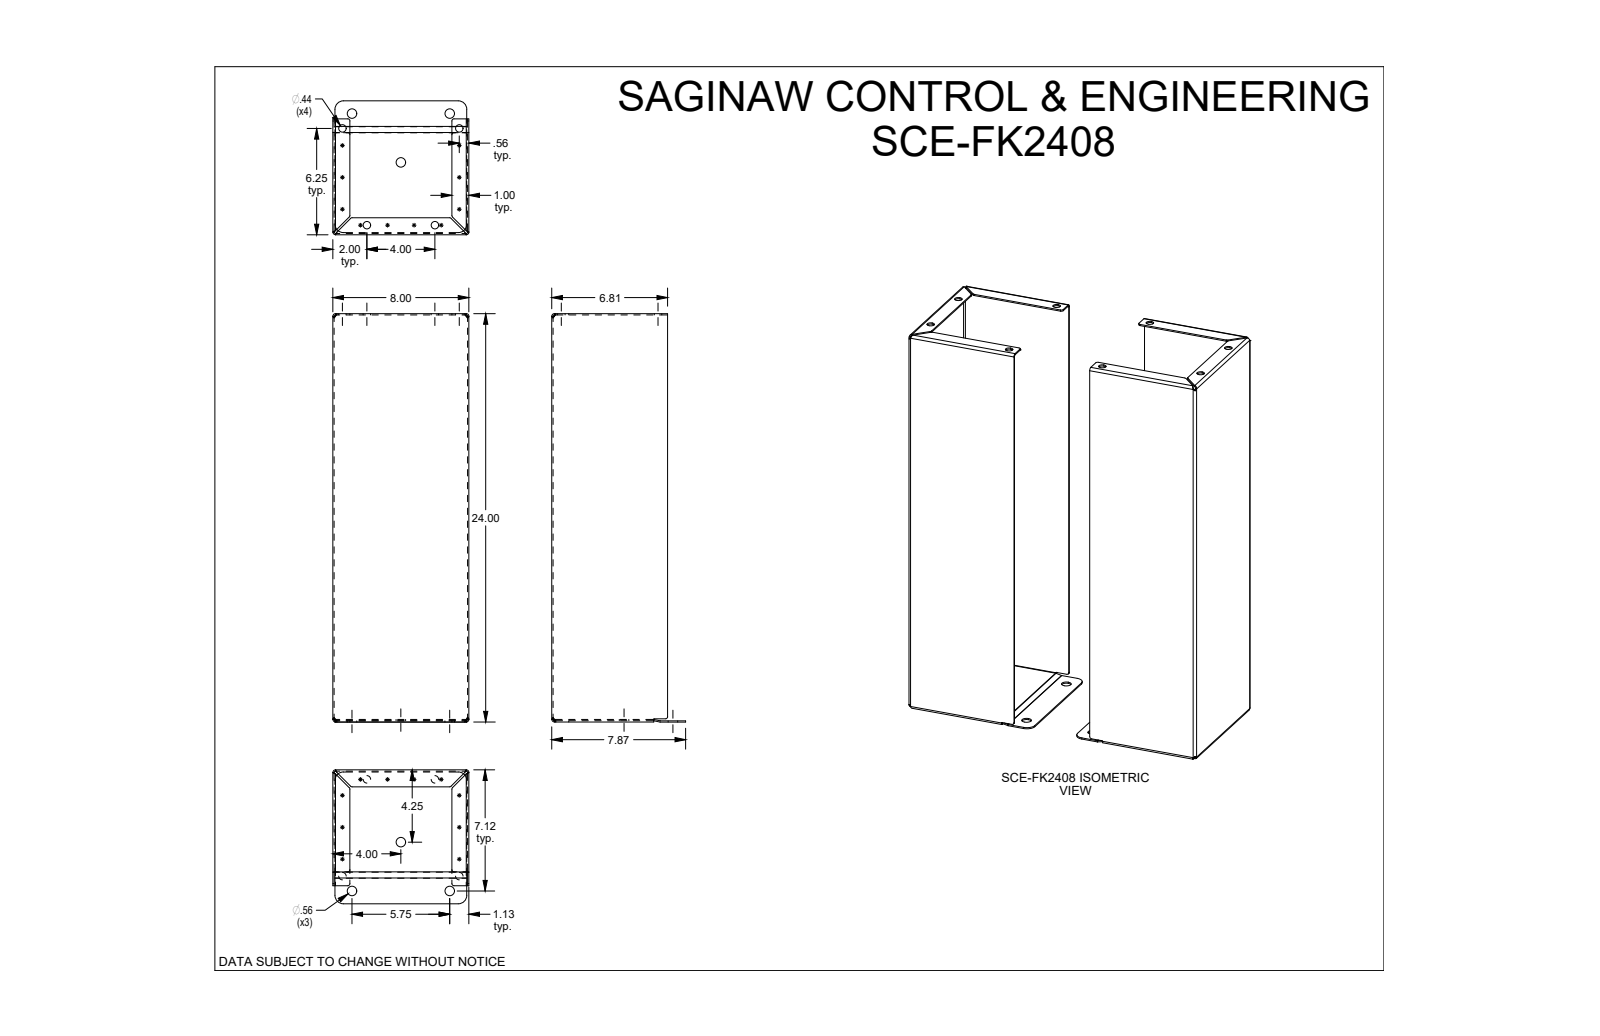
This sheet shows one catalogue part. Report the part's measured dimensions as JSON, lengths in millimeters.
{"part_name": "SCE-FK2408", "step_written_by": "SolidWorks 2019 (CONFIG_CONTROL_DESIGN)", "units": "millimeters", "bodies": {"solids": 4, "faces": 222, "planar": 96, "cylindrical": 94, "other": 32}, "overall_size": [609.7, 469.9, 203.2], "volume_mm3": 1482000, "surface_area_mm2": 1569000, "round_holes": [[11.1, 8], [14.3, 6]], "partial_cylinders_radius": [[3.2, 18], [2, 12], [3.9, 12], [12.7, 8], [3.5, 4], [0.5, 2], [1.6, 2], [1.6, 2]], "face_to_face_distances": [1.9, 1.9, 201.3, 468, 203.2, 469.9, 466.1, 199.4, 199.4, 201.3], "hole_center_spacings": [101, 106.6, 131, 149, 168.1, 195.1, 199.9, 221.1]}
